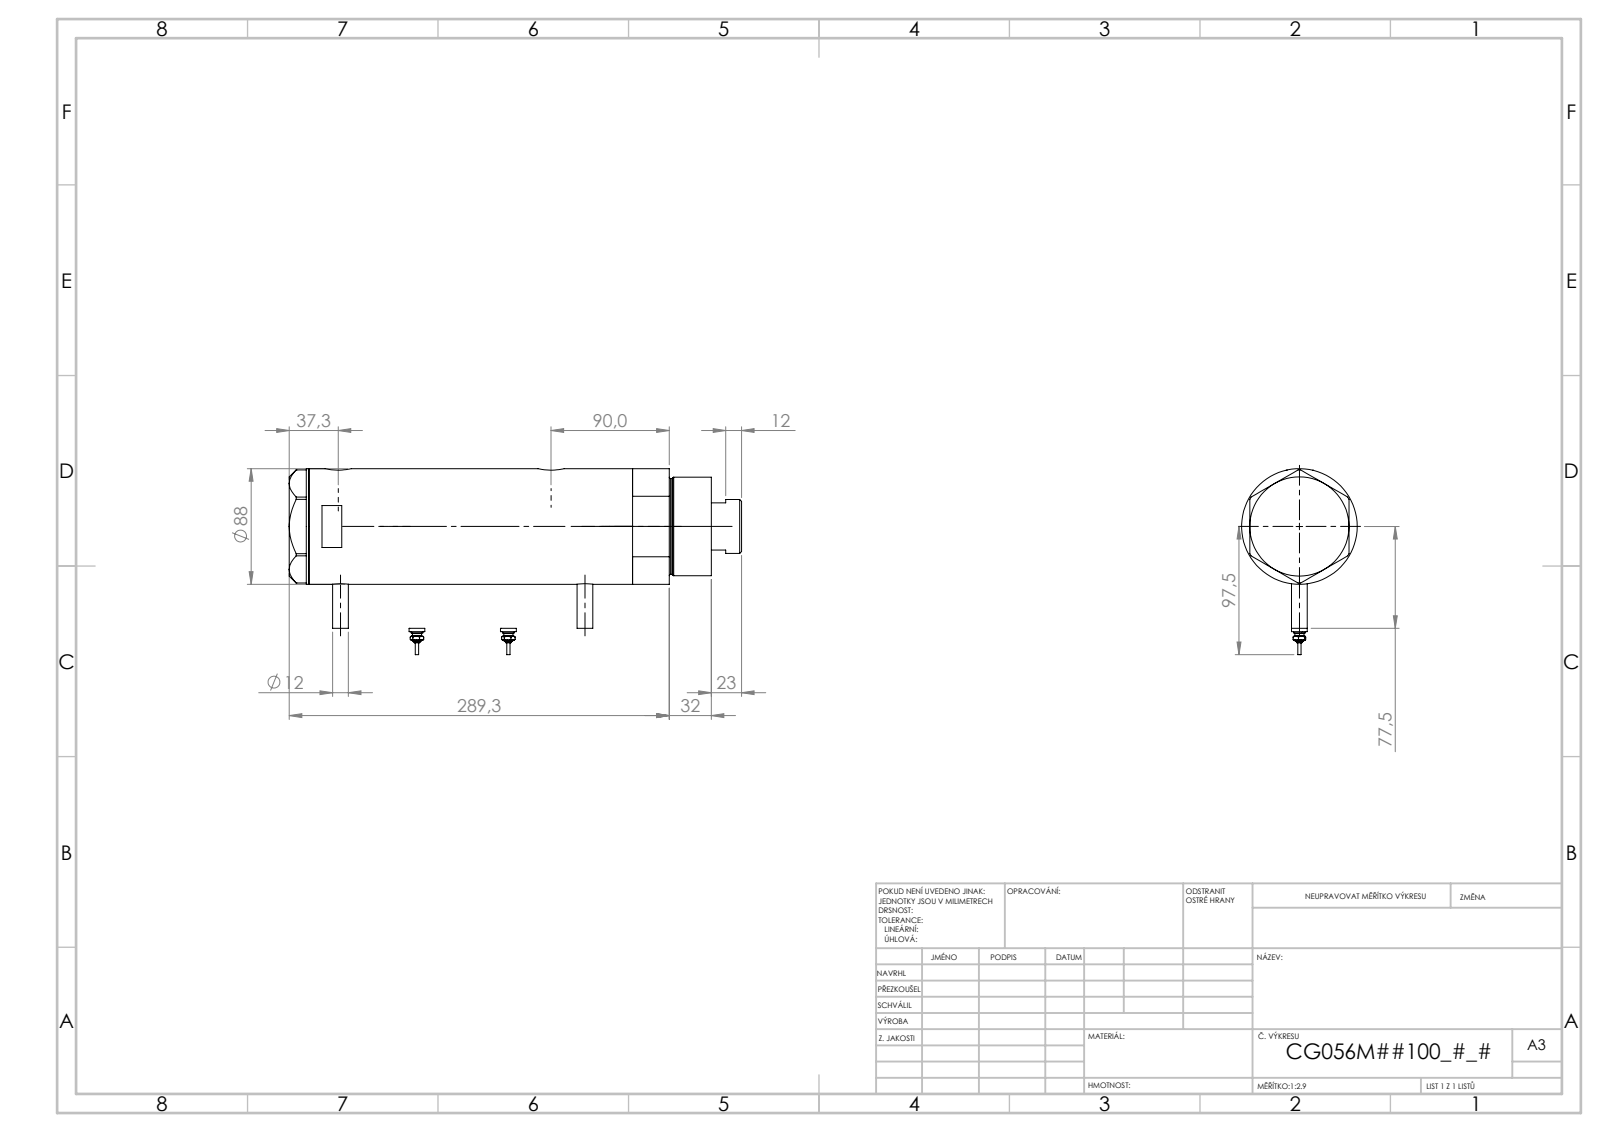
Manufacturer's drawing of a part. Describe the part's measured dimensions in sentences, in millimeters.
The part is named "V270CG_MIDDLE; V270CG_FRONT; V270CG_BACK; V270CG_SWITCH (+1 more)". Its 3-D file was written by "SolidWorks 2019 (CONFIG_CONTROL_DESIGN)". It is 6 solids with 232 faces: 81 planar, 77 cylindrical and 74 other. Overall it measures 324.47 by 120.3 by 88 millimeters. Its volume is 1 665 000 cubic millimeters and its surface area 240 640 square millimeters. Round holes: 2 of diameter 5, 2 of diameter 12.5, 2 of diameter 13.16, 2 of diameter 20, 1 of diameter 14.5, 1 of diameter 42, 1 of diameter 43.5, 1 of diameter 56, 1 of diameter 60, 1 of diameter 80. Round bosses or shafts: 2 of diameter 12, 2 of diameter 9, 2 of diameter 7, 2 of diameter 4.34, 2 of diameter 2.4, 1 of diameter 88, 1 of diameter 75, 1 of diameter 73. The main face-to-face distances are 174.4, 26, 148.4, 15, 41, 189.4, 286.47, 301.47, 260.47, 112.07. The hole center spacings are 1.7, 25.8, 150.3, 152, 176.1, 177.8.
